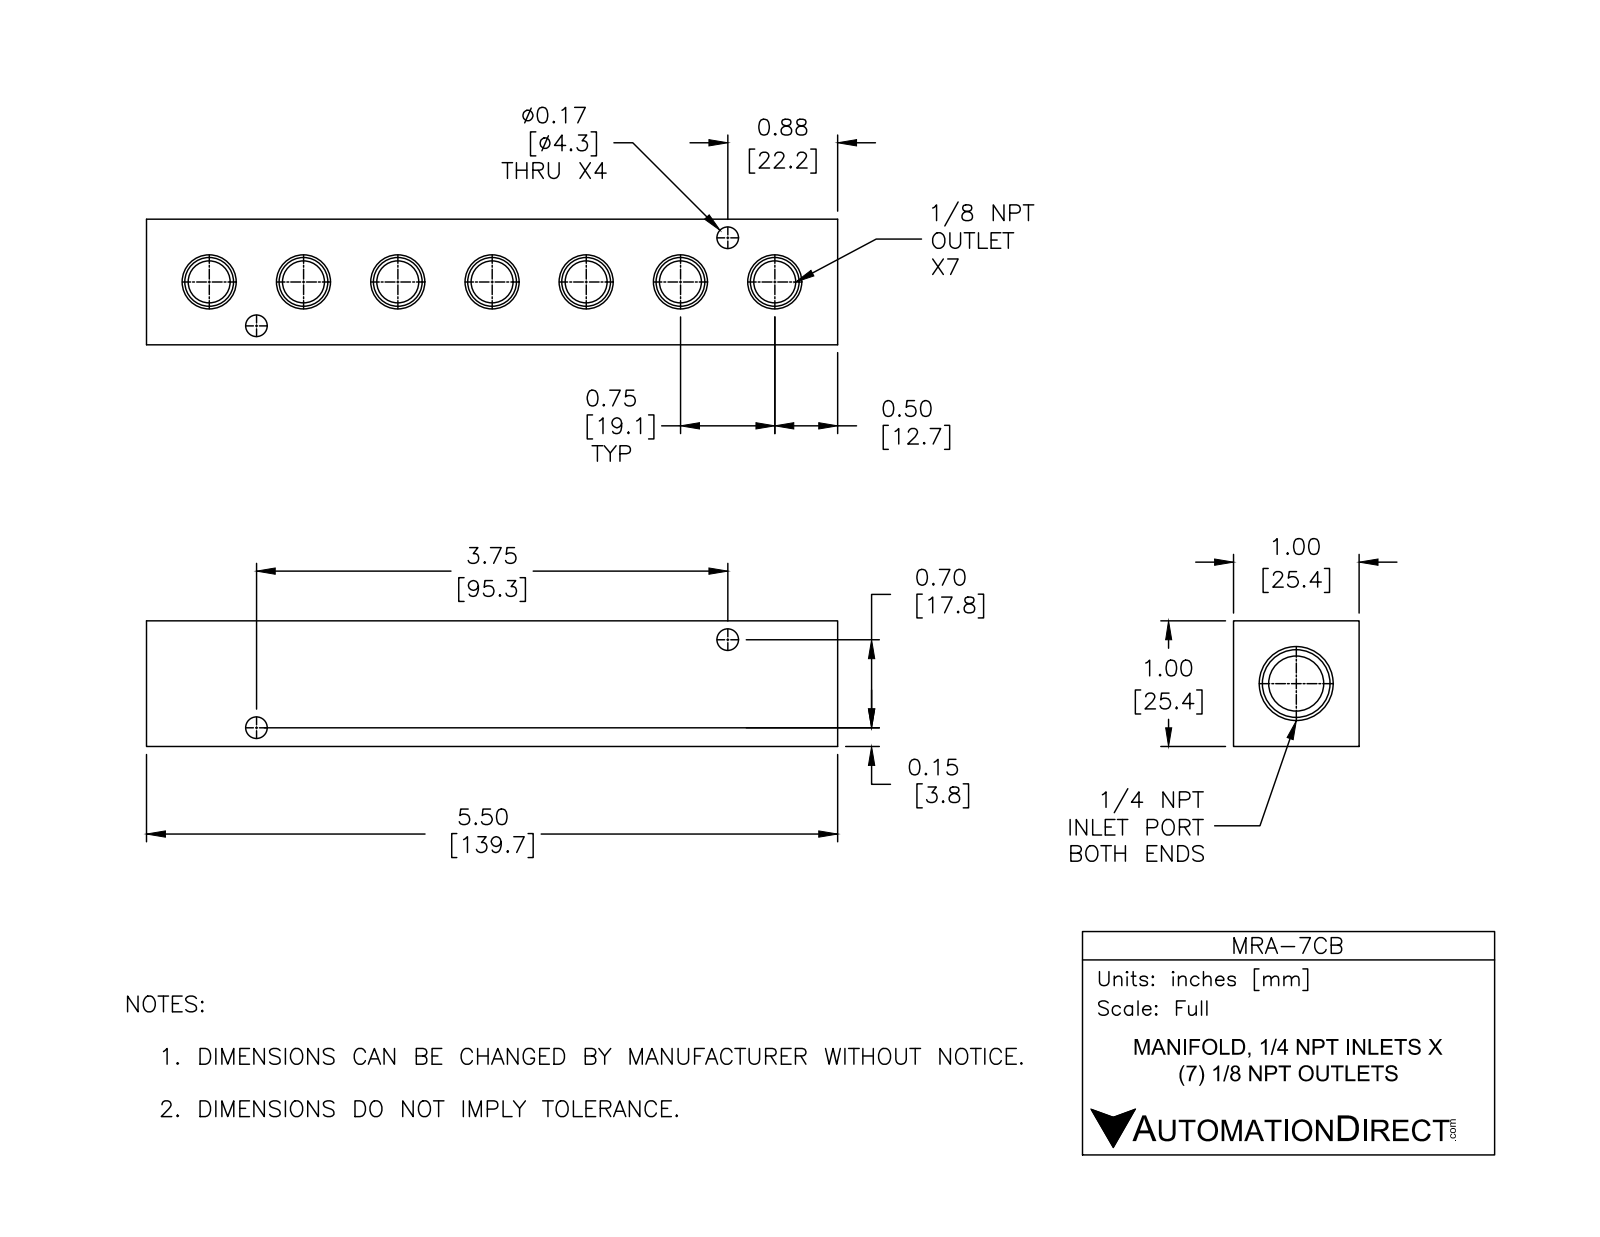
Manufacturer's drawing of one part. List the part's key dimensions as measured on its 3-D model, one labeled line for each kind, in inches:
Part name (STEP PRODUCT): MRA-7CB
STEP written by: SolidWorks 2015 (CONFIG_CONTROL_DESIGN)
Units: inches
Bodies: 1 solid, 82 faces (15 planar, 31 cylindrical, 36 other)
Overall size (bounding box): 5.5 × 1 × 1
Volume: 4.28 in³ · Surface area: 34.36 in²
Round holes (diameter × count): ⌀0.332 ×5, ⌀0.17 ×4, ⌀0.438 ×1
Partial cylindrical surfaces — rounded edges, fillets, slot ends (radius × count): R0.166 ×2
Main face-to-face distances: 1, 5.5, 0.73, 0.27, 0.39, 5.11, 4.72
Hole centre spacings: 0.75, 1.5, 0.513, 1.178, 1.907, 2.25, 2.648, 3.393
